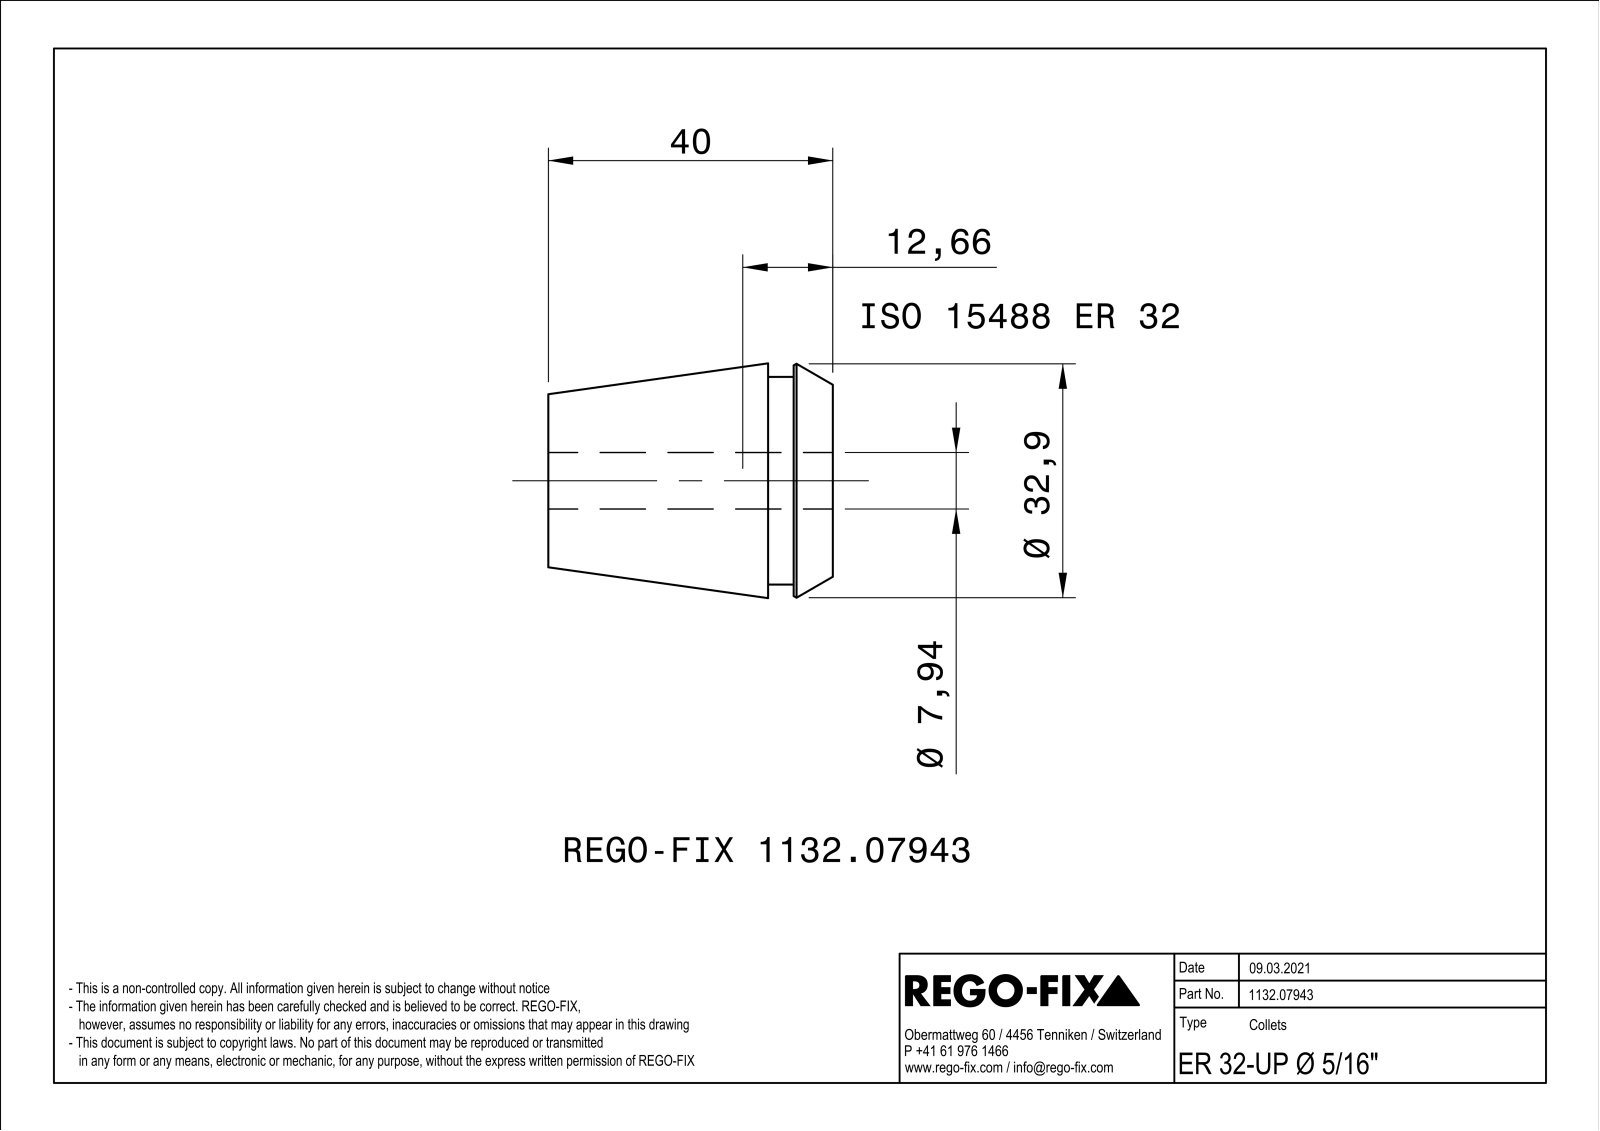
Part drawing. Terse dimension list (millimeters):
name: NOCUT
written by: SIEMENS PLM Software Solid Edge ST10 (AUTOMOTIVE_DESIGN)
unit: mm
bodies: 1 solid, 177 faces (72 planar, 25 cylindrical, 80 other)
size: 40 × 32.99 × 32.99
volume: 19 677 mm³; area: 16 972 mm²
holes: 1× ⌀7.94
bosses: 1× ⌀29.2
rounds: 8× R0.4
face distances: 0.8, 40, 9.1, 30.9, 5.5, 3.6, 34.5
